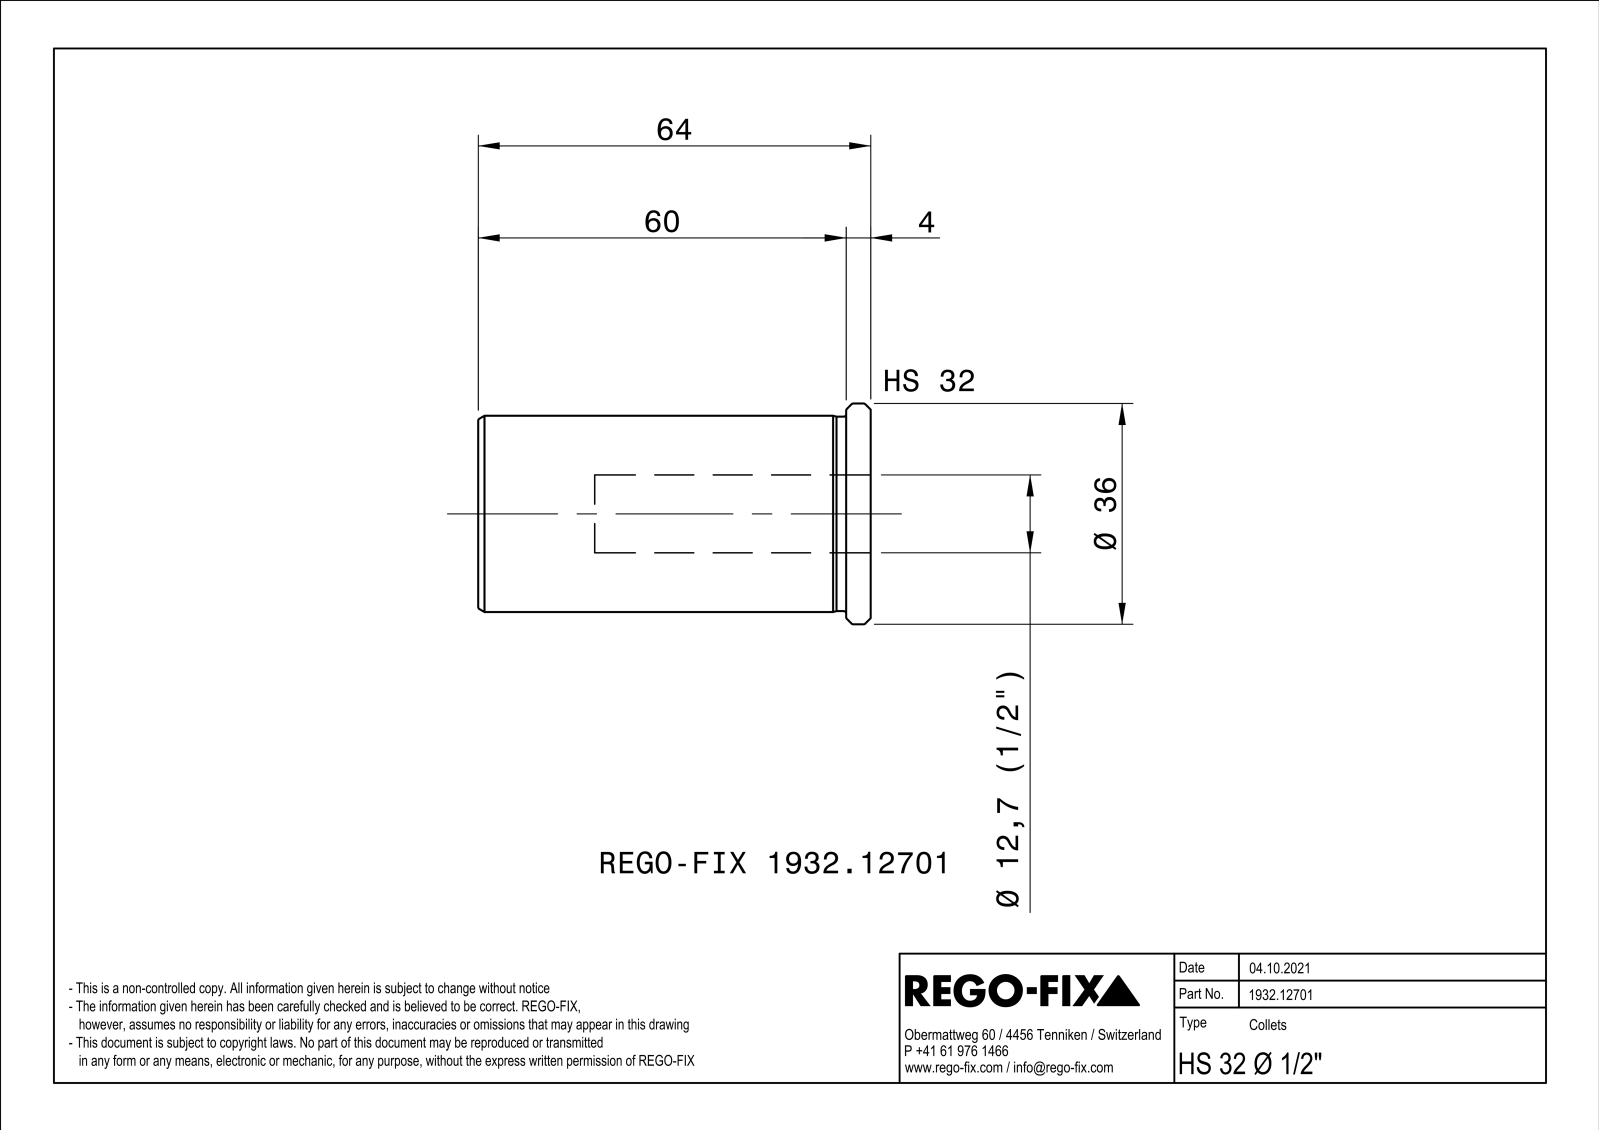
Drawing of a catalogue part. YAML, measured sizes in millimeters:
part_name: "NOCUT"
step_written_by: "SIEMENS PLM Software Solid Edge ST10 (AUTOMOTIVE_DESIGN)"
units: millimeters
bodies: {solids: 1, faces: 70, planar: 22, cylindrical: 11, other: 37}
overall_size: [64, 35.99, 35.99]
volume: 36022
surface_area: 14024
round_holes:
  - {diameter: 12.7, count: 1}
  - {diameter: 26.5, count: 1}
round_bosses_or_shafts:
  - {diameter: 36, count: 1}
  - {diameter: 32, count: 1}
  - {diameter: 31.7, count: 1}
face_to_face_distances: [1, 64, 4, 60]
